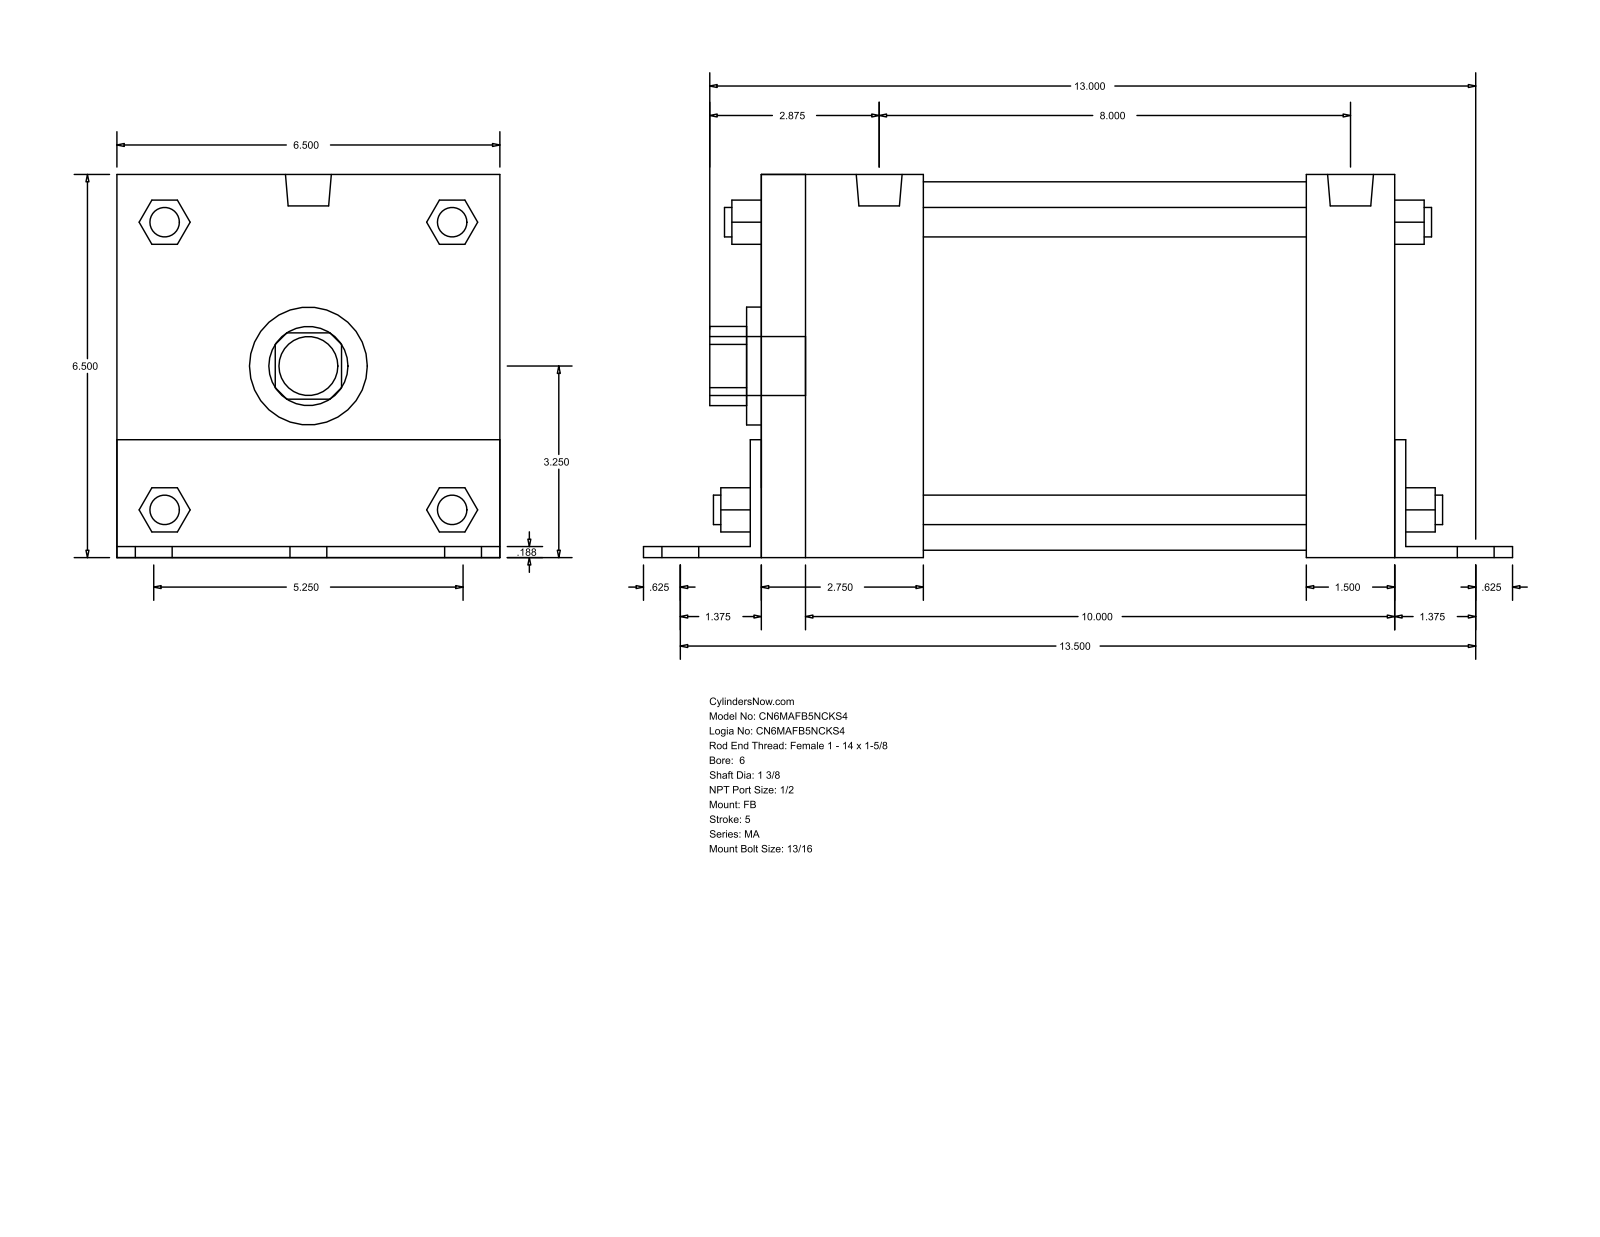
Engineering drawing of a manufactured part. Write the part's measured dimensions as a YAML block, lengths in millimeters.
part_name: "MA_FB__0600_1.375"
step_written_by: "GSSL Pune (CONFIG_CONTROL_DESIGN)"
units: millimeters
bodies: {solids: 0, faces: 140, planar: 105, cylindrical: 35, other: 0}
overall_size: [371.48, 165.15, 165.1]
round_holes:
  - {diameter: 34.92, count: 1}
  - {diameter: 50.8, count: 1}
  - {diameter: 158.75, count: 1}
round_bosses_or_shafts:
  - {diameter: 20.64, count: 6}
  - {diameter: 17.46, count: 4}
  - {diameter: 12.7, count: 4}
  - {diameter: 19.77, count: 2}
  - {diameter: 25.4, count: 1}
partial_cylinders:
  - {radius: 17.06, count: 1}
  - {radius: 32.05, count: 1}
face_to_face_distances: [165.1, 4.76, 269.87, 165.15, 4.71, 160.39, 4.77, 38.1, 274.64, 279.4]
